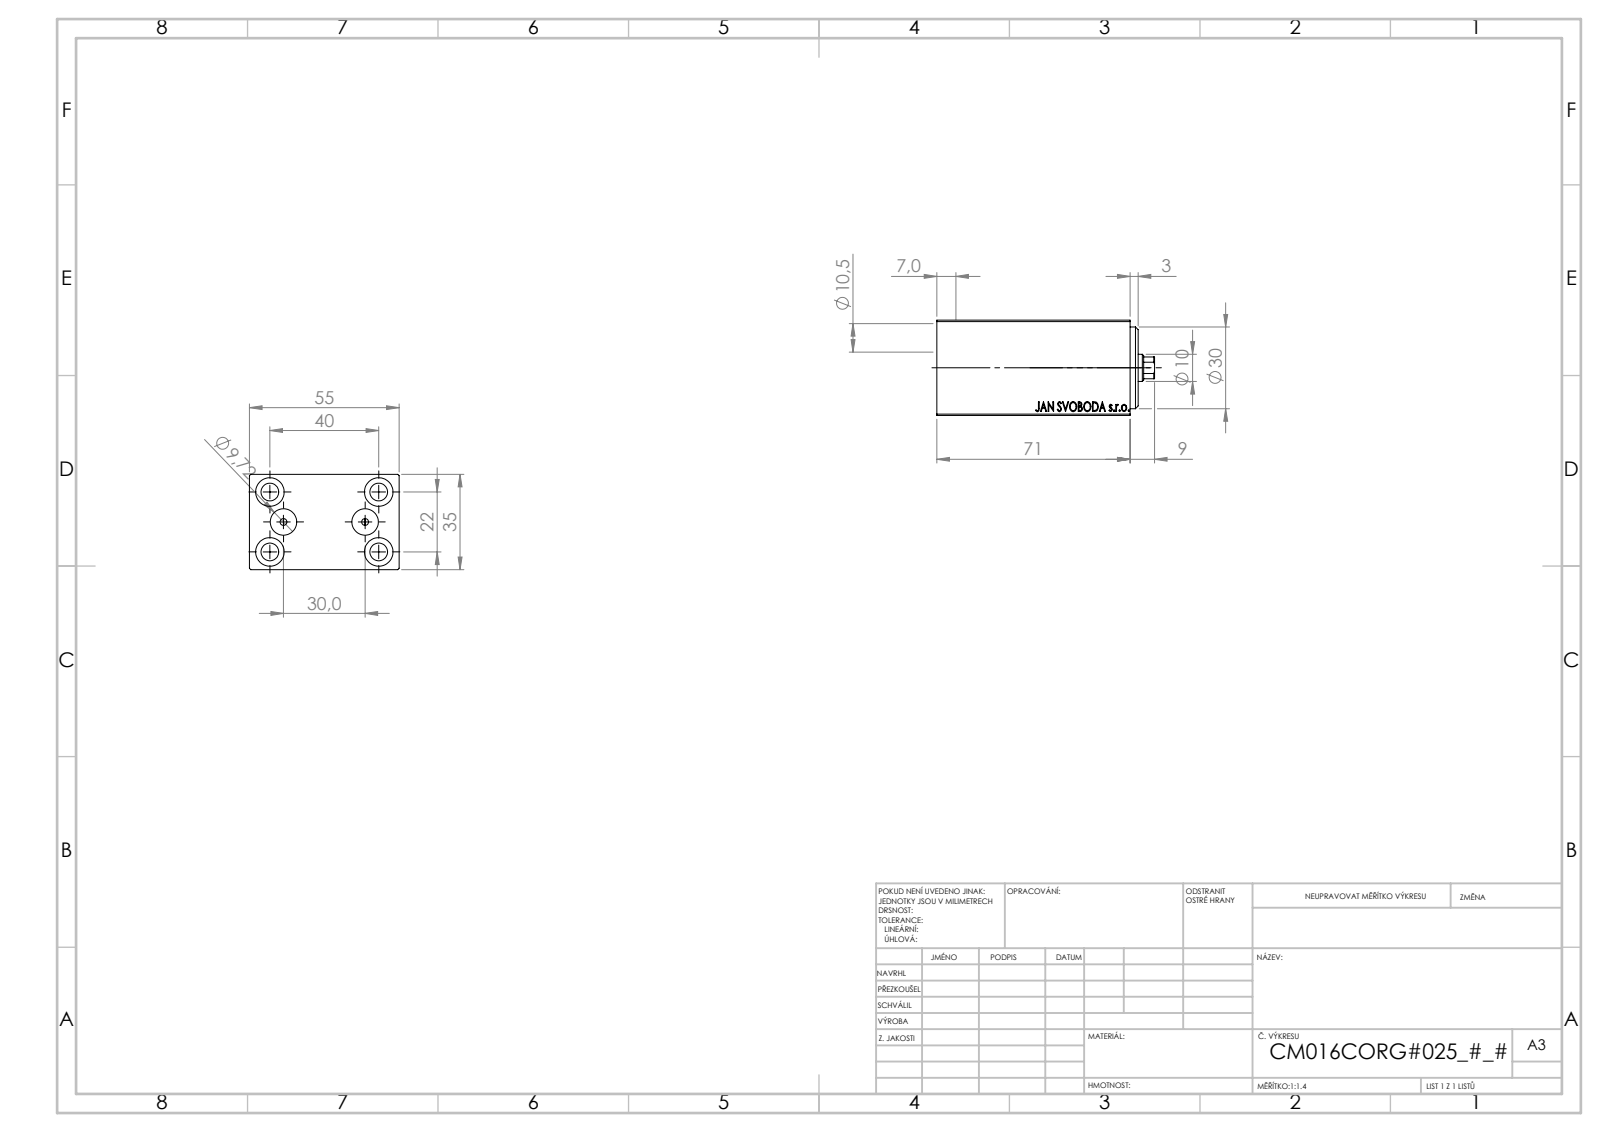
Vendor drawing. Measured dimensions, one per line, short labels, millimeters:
name: V450CM_VC_B; V450CM_C_VCP; V450CM_C_Body
written by: SolidWorks 2019 (CONFIG_CONTROL_DESIGN)
unit: mm
bodies: 3 solids, 861 faces (409 planar, 58 cylindrical, 394 other)
size: 80 × 55 × 35
volume: 121 226 mm³; area: 31 979 mm²
holes: 4× ⌀6.5, 4× ⌀10.5, 2× ⌀2.5, 2× ⌀9.72, 1× ⌀4.5, 1× ⌀10, 1× ⌀13.5, 1× ⌀14.5, 1× ⌀16, 1× ⌀18, 1× ⌀30
rounds: 1× R4.5
face distances: 35, 55, 5, 66, 3, 71, 10, 64, 8, 74
hole spacings: 12.08, 22.83, 36.69, 15, 22, 40, 45.65, 30
